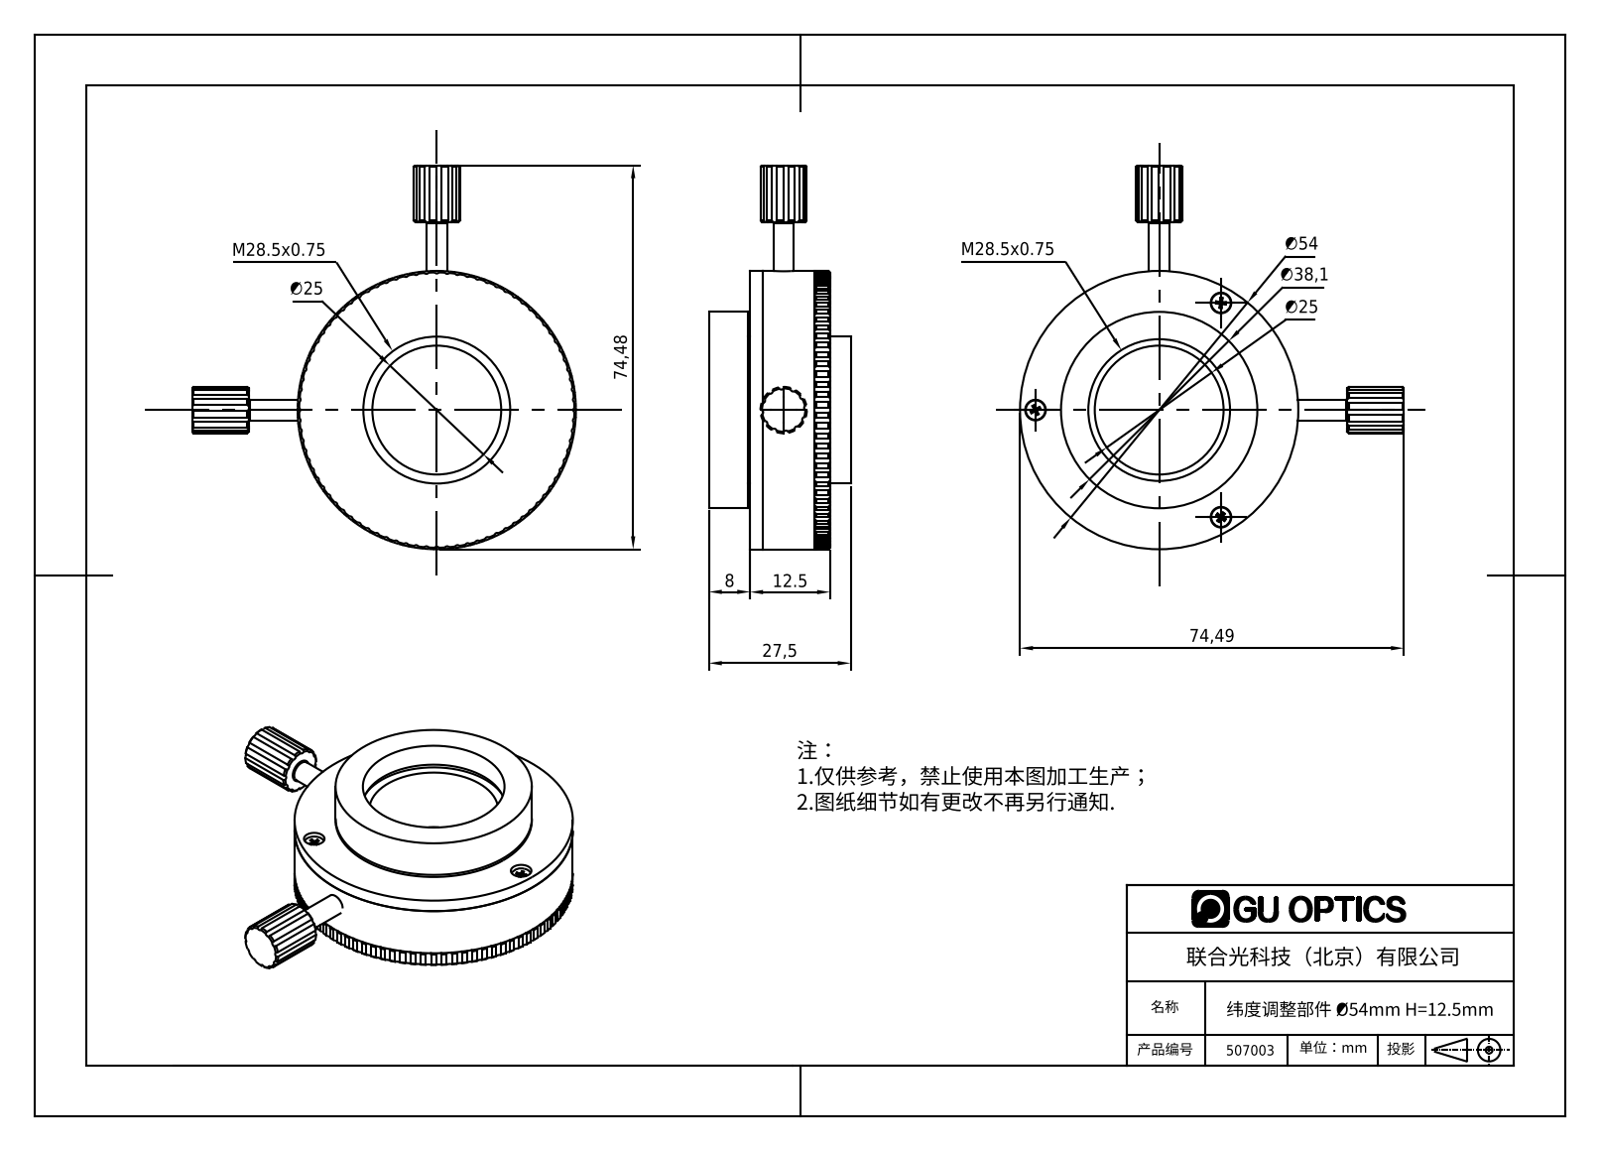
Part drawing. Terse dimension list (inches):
name: 507003
written by: SolidWorks 2020 (CONFIG_CONTROL_DESIGN)
unit: in
bodies: 10 solids, 685 faces (70 planar, 347 cylindrical, 268 other)
size: 2.933 × 2.933 × 1.083
volume: 1.876 in³; area: 36.35 in²
holes: 3× ⌀0.063, 3× ⌀0.094, 3× ⌀0.157, 2× ⌀0.13, 1× ⌀0.039, 1× ⌀0.205, 1× ⌀0.244, 1× ⌀0.984, 1× ⌀1.083, 1× ⌀1.5, 1× ⌀1.772
bosses: 3× ⌀0.079, 3× ⌀0.055, 2× ⌀0.157, 1× ⌀2.126, 1× ⌀1.614, 1× ⌀1.122, 1× ⌀0.236
rounds: 108× R0.02, 2× R0.177
face distances: 0.394, 0.315, 0.512, 0.118, 0.079, 0.197, 0.413, 0.098, 0.61, 0.492
hole spacings: 0.945, 1.637
